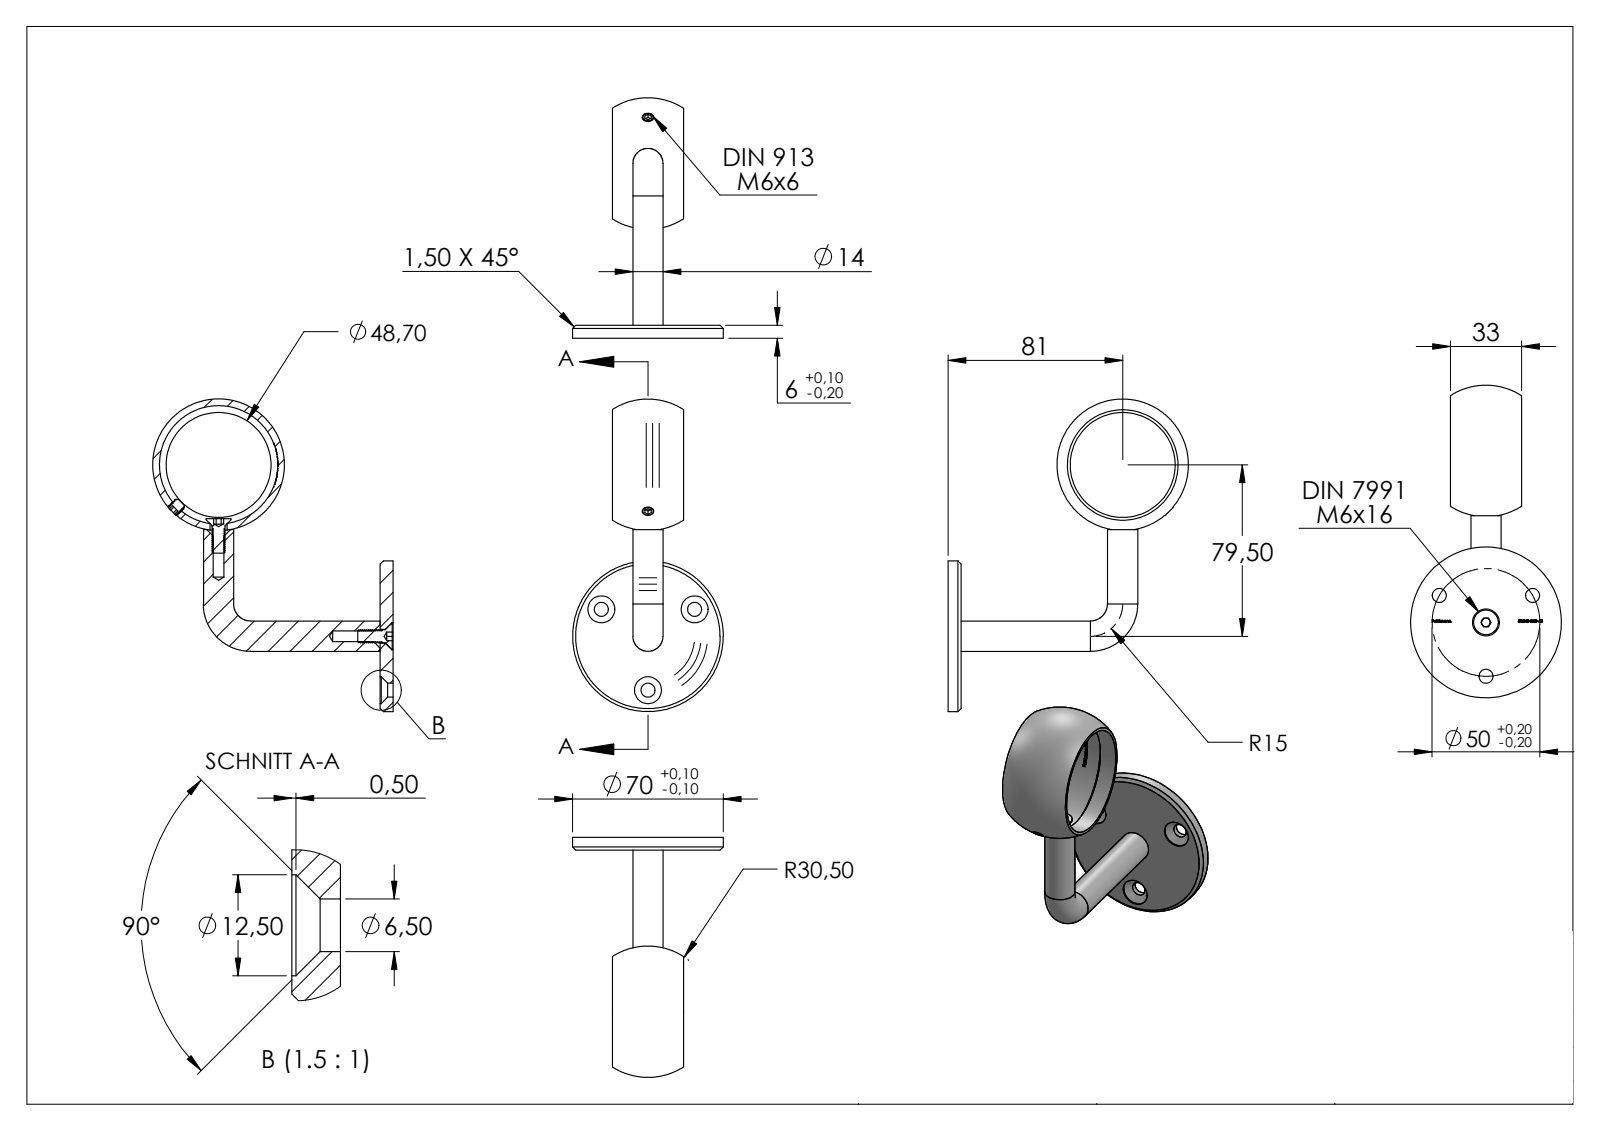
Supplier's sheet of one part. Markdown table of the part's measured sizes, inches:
| quantity | value |
| --- | --- |
| part name | socket countersunk head screw_din; 5024X-240 Teil1; socket set screw flat point_din_DIN 913 - M6 x 6-S; 50251-240_50251-240 (+7 more) |
| STEP written by | SolidWorks 2018 (CONFIG_CONTROL_DESIGN) |
| units | inches |
| bodies | 6 solids, 831 faces (312 planar, 129 cylindrical, 390 other) |
| overall size | 5.709 × 4.39 × 2.756 |
| volume | 3.49 in³ |
| surface area | 45.43 in² |
| round holes (diameter × count) | 0.256 × 4, 0.492 × 4, 0.197 × 3, 0.315 × 1, 1.917 × 1, 2.165 × 1 |
| round bosses / shafts (diameter × count) | 0.236 × 3, 0.551 × 2, 0.456 × 2, 2.756 × 1 |
| partial cylindrical surfaces (radius × count) | 1.087 × 1 |
| main face-to-face distances | 0.236, 1.299, 0.018, 0.219, 0.199, 0.63, 0.158, 0.648, 0.411, 0.431 |
| hole center spacings | 0.984, 1.705 |
